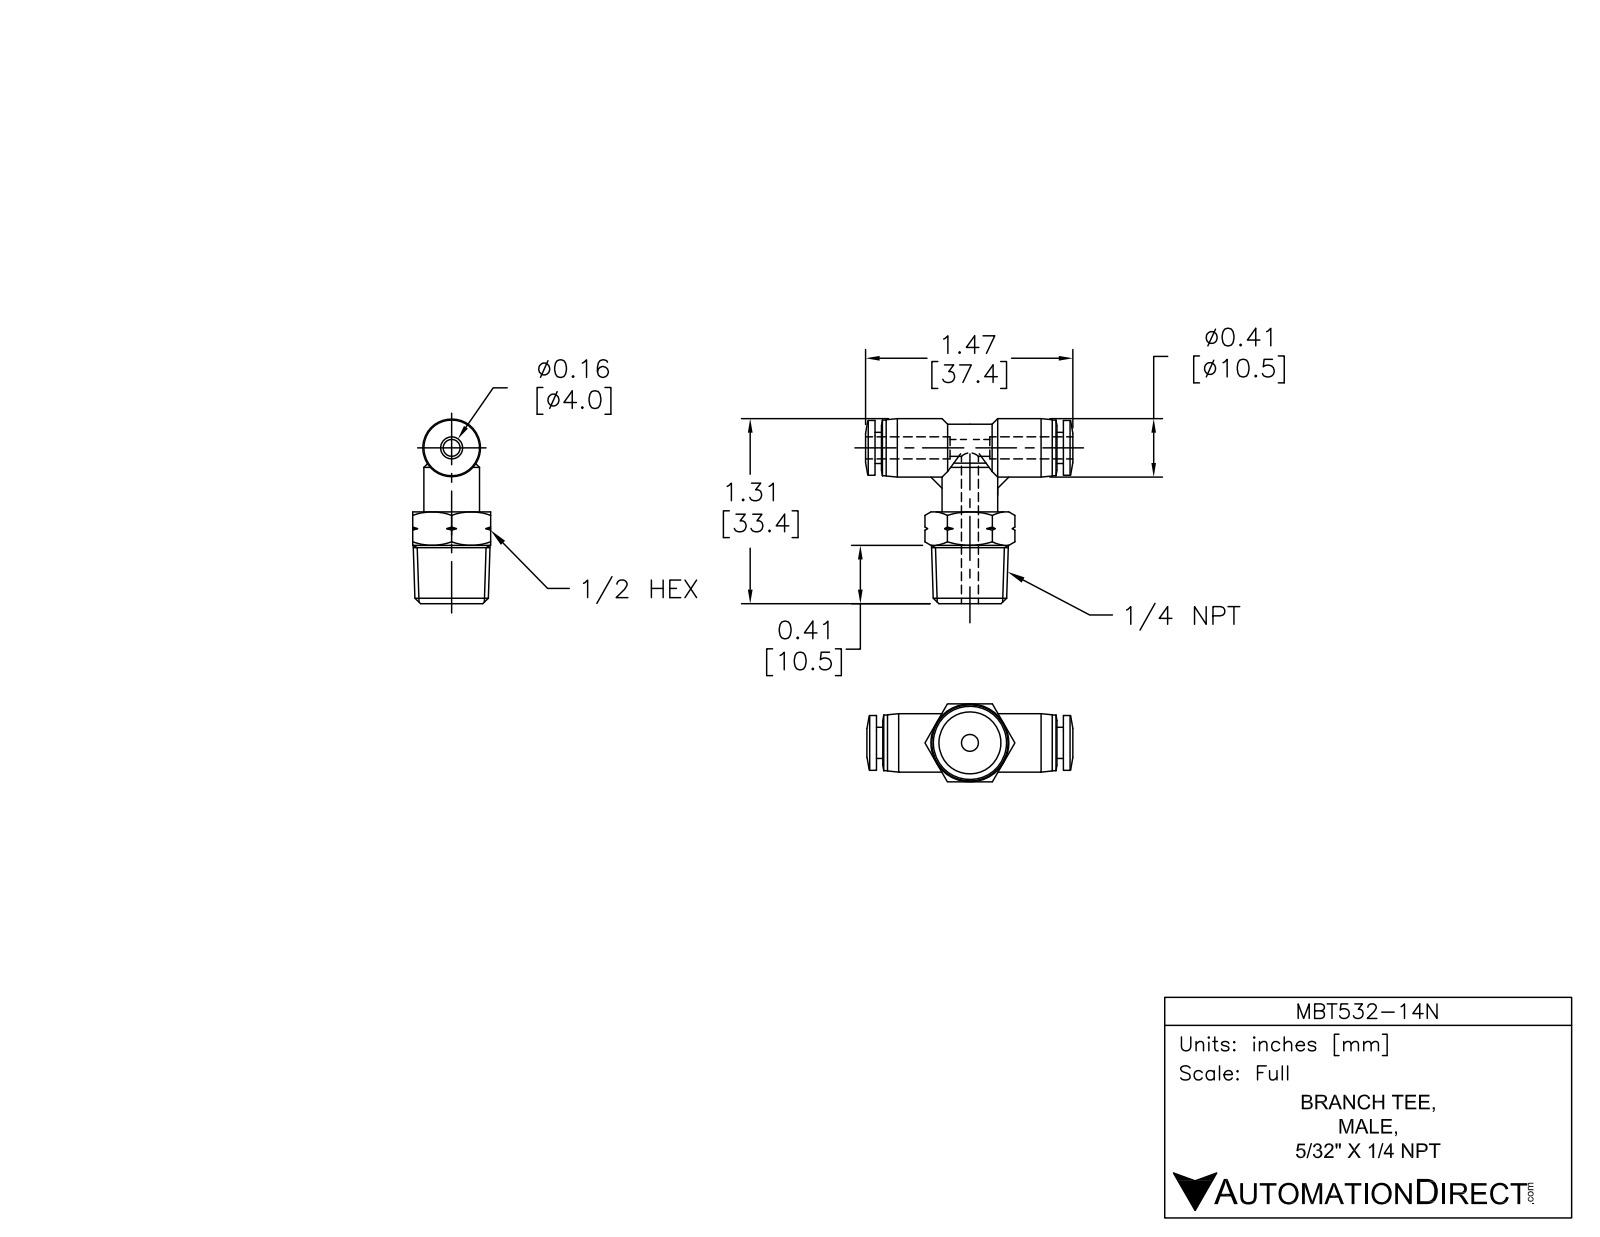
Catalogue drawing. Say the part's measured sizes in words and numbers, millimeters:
The part is named "MBT532-14N". Its 3-D file was written by "SolidWorks 2015 (AUTOMOTIVE_DESIGN)". It is 1 solid with 114 faces: 23 planar, 30 cylindrical and 61 other. Overall it measures 37 by 33.2 by 14 millimeters. Its volume is 5 100 cubic millimeters and its surface area 3 301 square millimeters. Round holes: 2 of diameter 3, 1 of diameter 4.3. Round bosses or shafts: 2 of diameter 10, 1 of diameter 10.5, 1 of diameter 9.9, 1 of diameter 8, 1 of diameter 5.6. Partial cylindrical surfaces (rounded edges, fillets, slot ends): 1 of radius 4. The main face-to-face distances are 14, 16.5, 33.6, 1.1, 32.5, 31.3, 13.1, 20.5, 11.9, 19.4.
